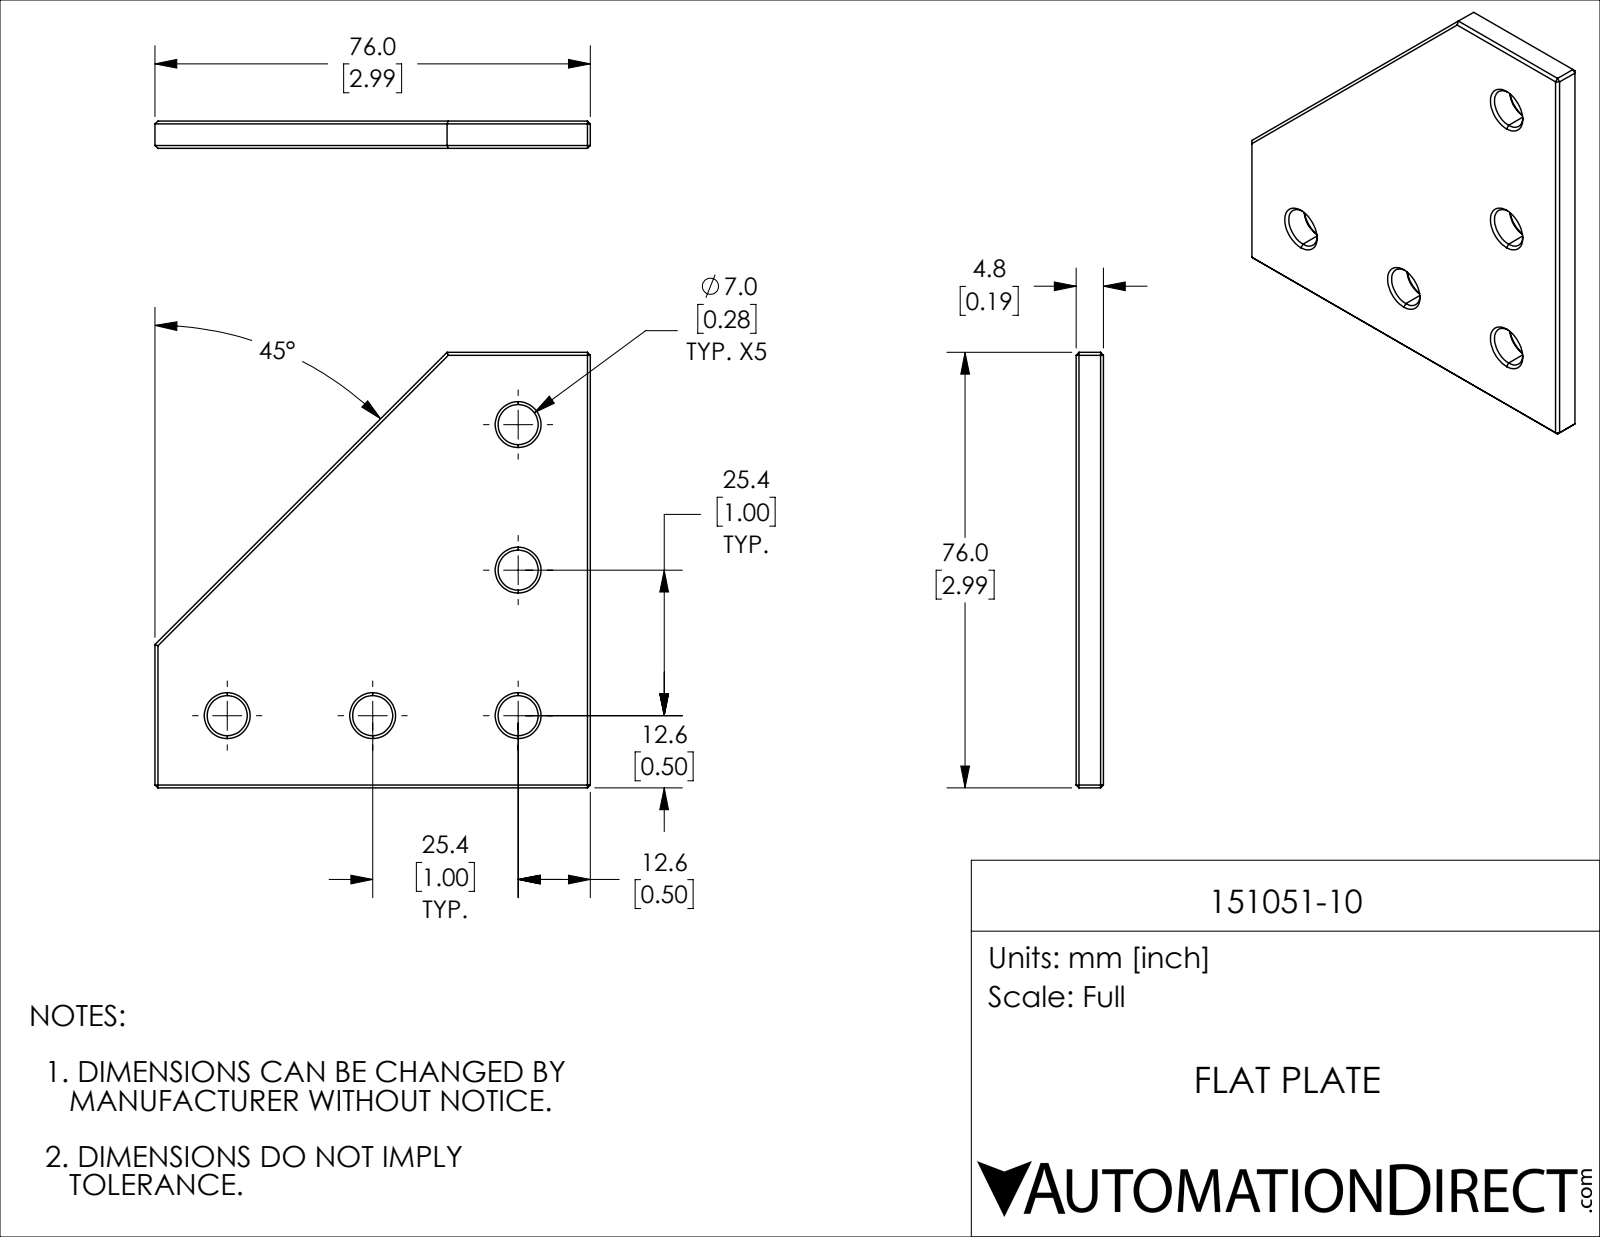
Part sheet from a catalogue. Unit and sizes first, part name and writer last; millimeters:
Units: millimetres
Overall size (bounding box): 76 × 76 × 4.76
Round holes (diameter × count): ⌀7 ×5
Main face-to-face distances: 4.76, 76, 56.39, 106.76, 71.06, 89.29
Hole centre spacings: 25.4, 50.8, 56.8, 35.92, 71.84
Volume: 20 300 mm³ · Surface area: 10 169 mm²
Bodies: 1 solid, 56 faces (26 planar, 10 cylindrical, 20 other)
Part name (STEP PRODUCT): 151051-10
STEP written by: SolidWorks 2024 (CONFIG_CONTROL_DESIGN)
